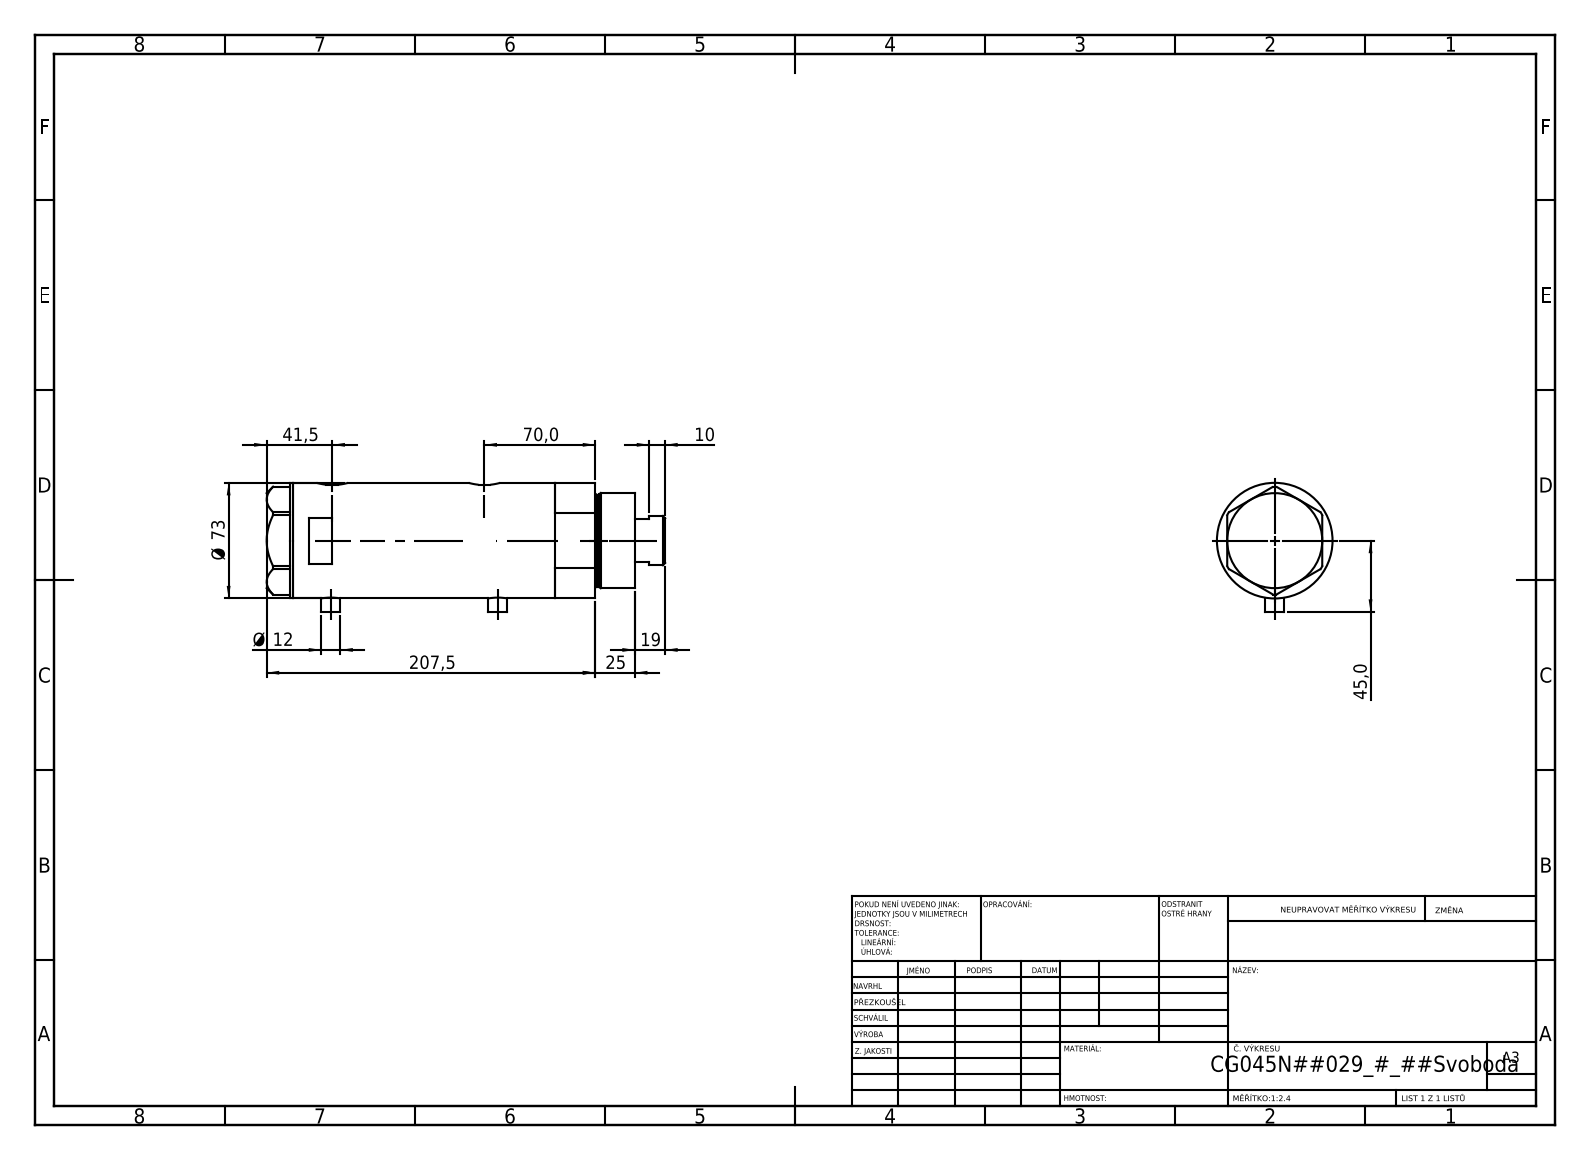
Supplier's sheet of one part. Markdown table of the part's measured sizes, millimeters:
| quantity | value |
| --- | --- |
| part name | V270CG_FRONT; V270CG_BACK; V270CG_MIDDLE; V270CG_VC |
| STEP written by | SolidWorks 2019 (CONFIG_CONTROL_DESIGN) |
| units | millimeters |
| bodies | 4 solids, 125 faces (50 planar, 55 cylindrical, 20 other) |
| overall size | 251.6 × 81.5 × 73 |
| volume | 900 553 mm³ |
| surface area | 150 139 mm² |
| round holes (diameter × count) | 5 × 2, 12.5 × 2, 13.16 × 2, 10.5 × 1, 32 × 1, 33.5 × 1, 45 × 1, 48 × 1, 64 × 1 |
| round bosses / shafts (diameter × count) | 12 × 2, 73 × 1, 60 × 1, 58 × 1, 31 × 1 |
| partial cylindrical surfaces (radius × count) | 10 × 2 |
| main face-to-face distances | 95, 121, 26, 16.5, 42.5, 137.5, 2, 216, 232.5, 190 |
| hole center spacings | 1, 8.5, 96, 97, 104.5, 105.5 |
